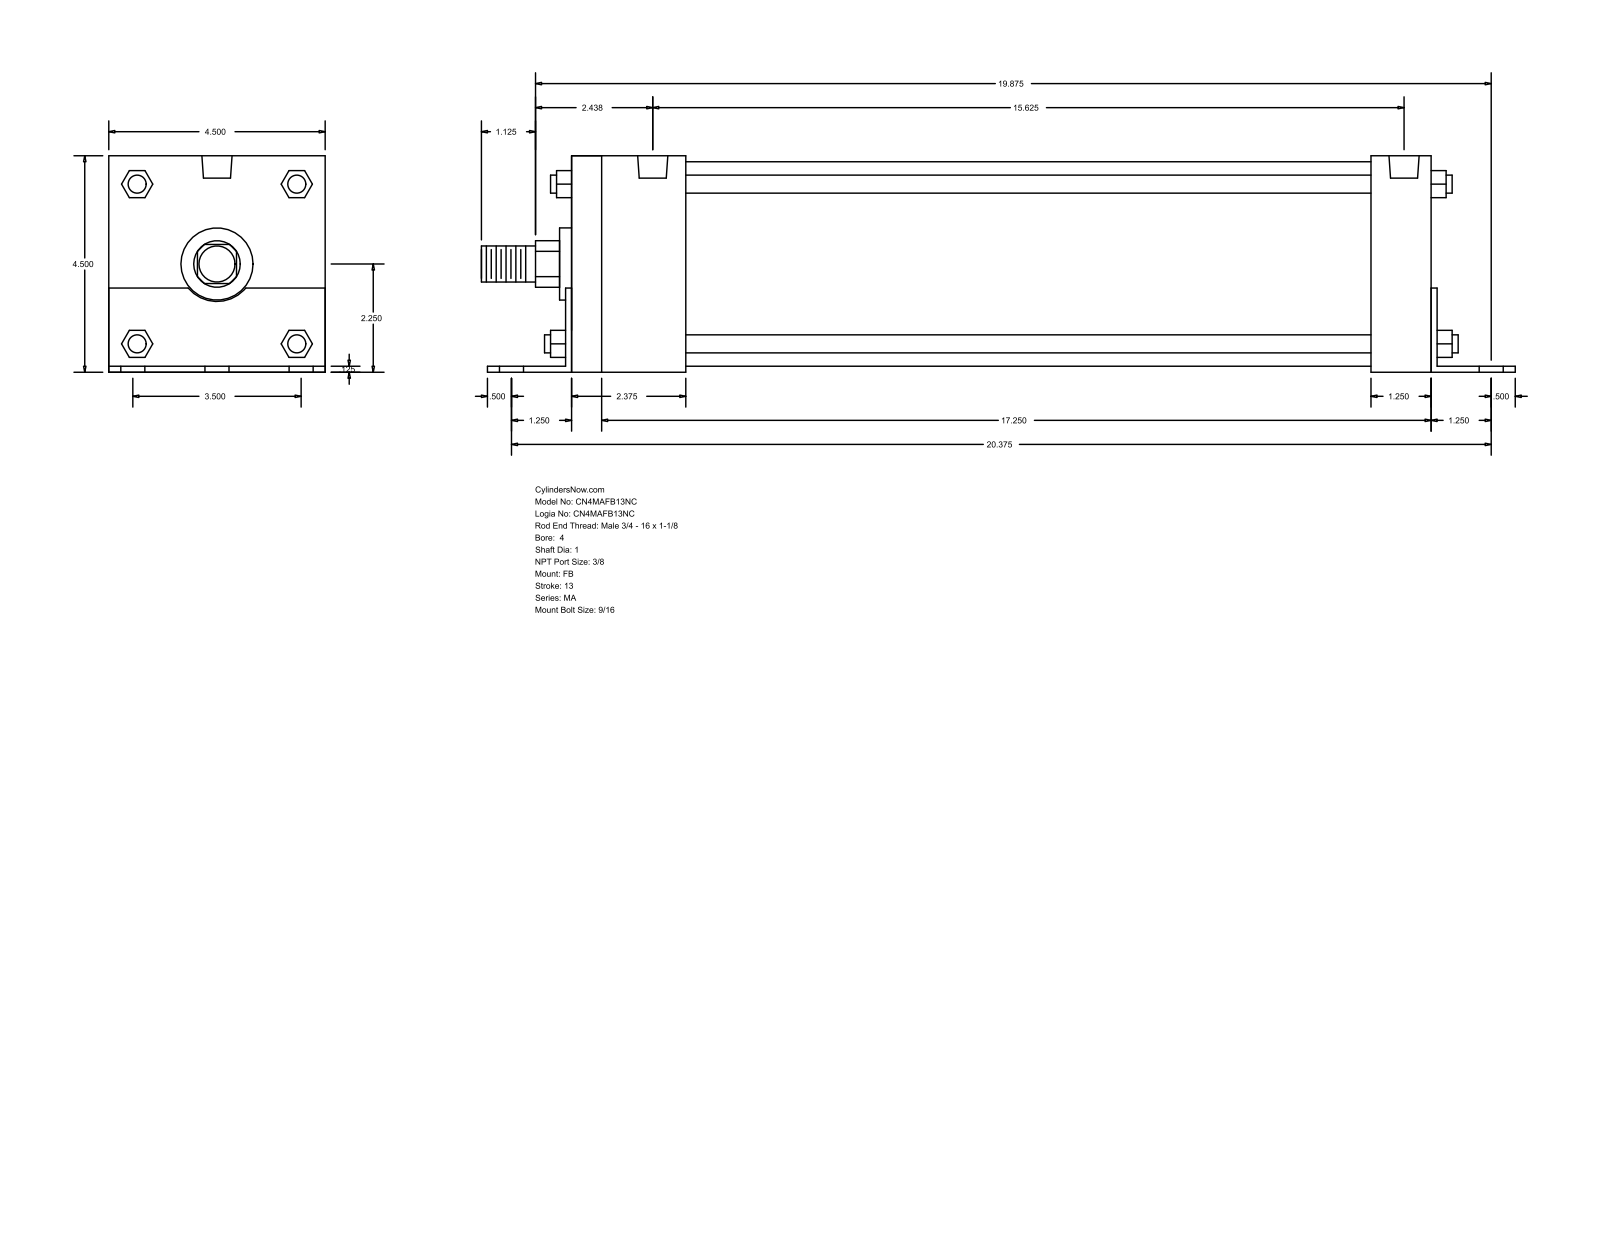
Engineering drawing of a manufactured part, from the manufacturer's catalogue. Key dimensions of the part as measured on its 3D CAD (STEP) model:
Part name (STEP PRODUCT): MA_FB__0400_1
STEP written by: GSSL Pune (CONFIG_CONTROL_DESIGN)
Units: millimetres
Bodies: 0 solids, 140 faces (105 planar, 35 cylindrical, 0 other)
Overall size (bounding box): 546.1 × 114.35 × 114.3
Round holes (diameter × count): ⌀14.29 ×6, ⌀11.11 ×4, ⌀15.93 ×2
Round bosses / shafts (diameter × count): ⌀9.53 ×4, ⌀107.95 ×1, ⌀38.1 ×1, ⌀25.4 ×1, ⌀19.05 ×1
Partial cylindrical surfaces — rounded edges, fillets, slot ends (radius × count): R12.29 ×1, R19.81 ×1
Main face-to-face distances: 114.3, 3.17, 114.35, 3.12, 111.18, 454.02, 3.18, 460.37, 457.2, 457.19
Hole centre spacings: 44.45, 519.43, 517.52, 63.99, 67.5, 86.85, 88.9, 90.97
